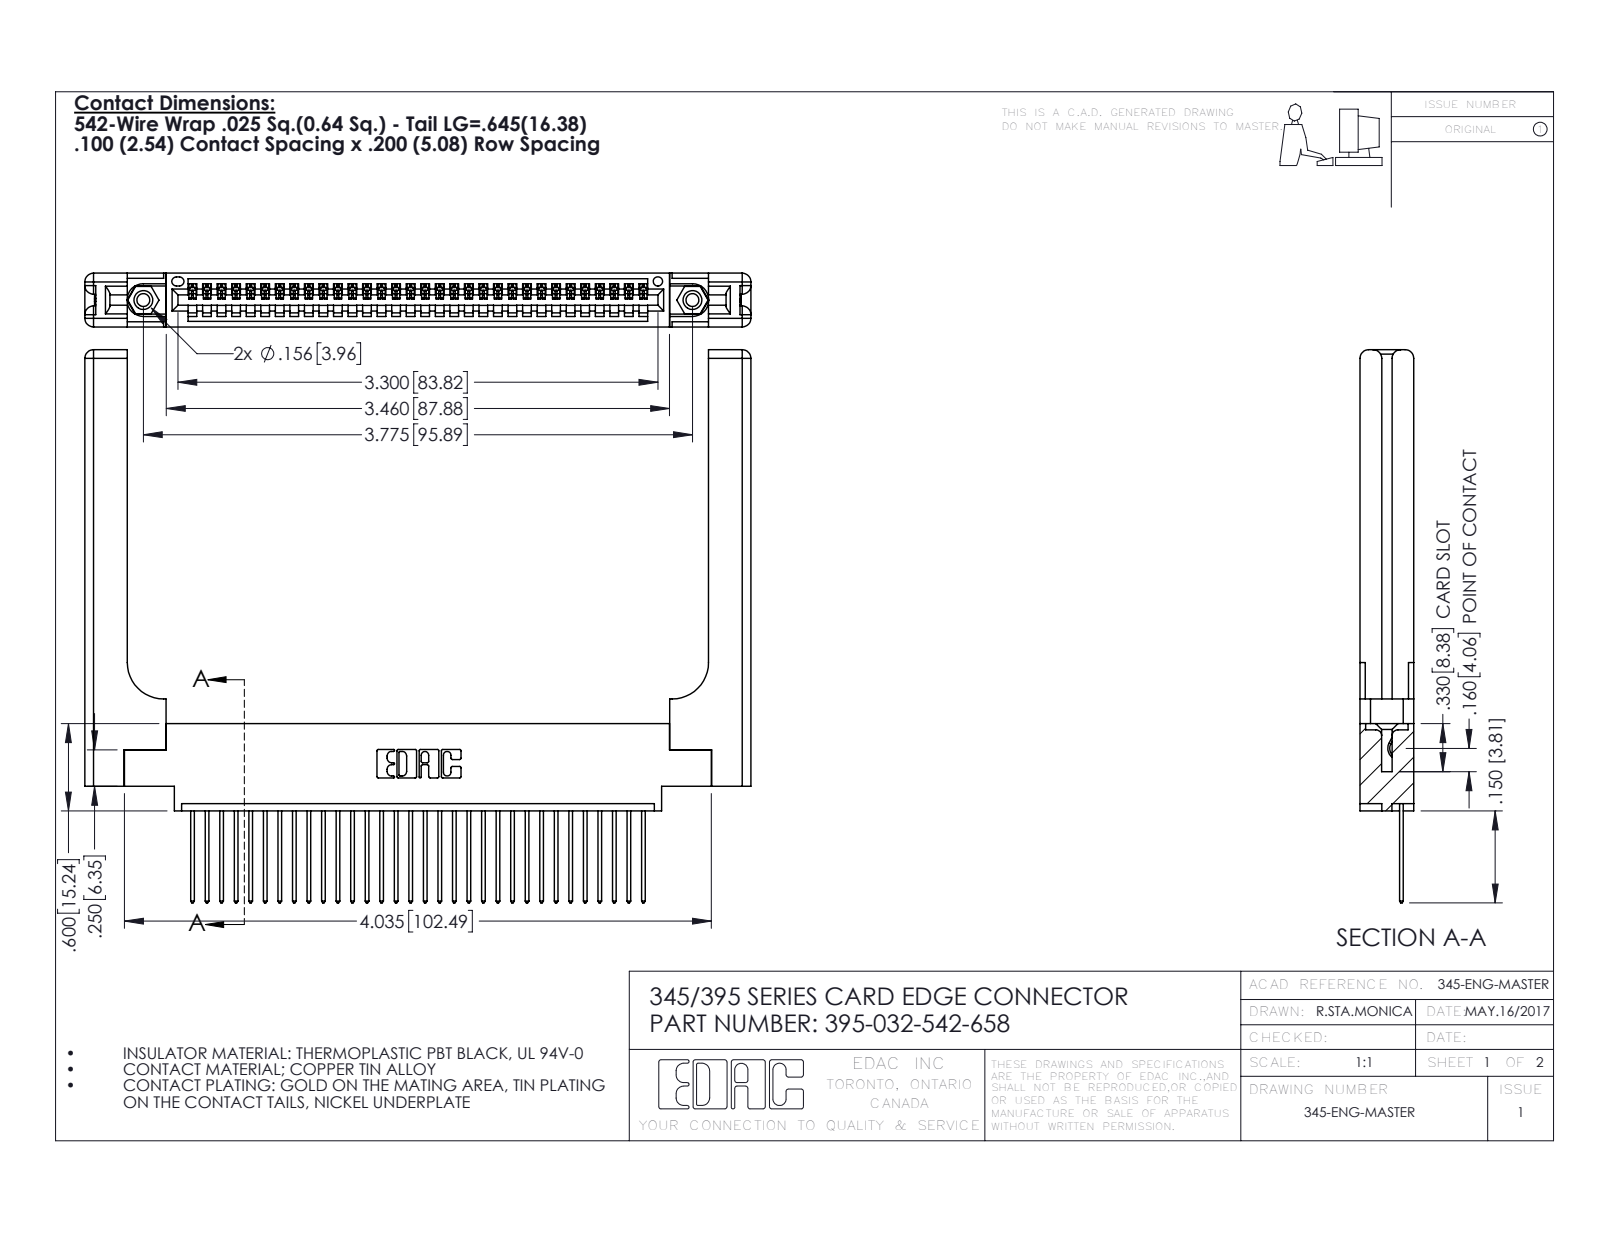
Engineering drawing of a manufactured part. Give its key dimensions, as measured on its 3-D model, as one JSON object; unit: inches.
{"part_name": "345-250-001_345-250-001-102; 345-292-001_345-293-142; 345-220-058_345-220-058; 345 Part_0.170 Offset - 0.156 Dia-TH (+1 more)", "step_written_by": "SolidWorks 2016 (CONFIG_CONTROL_DESIGN)", "units": "inches", "bodies": {"solids": 37, "faces": 2242, "planar": 1512, "cylindrical": 670, "other": 60}, "overall_size": [4.579, 3.802, 0.37], "volume_in3": 1.186, "surface_area_in2": 31.41, "round_holes": [[0.089, 2], [0.125, 2], [0.156, 2], [0.064, 1]], "round_bosses_or_shafts": [[0.155, 2]], "partial_cylinders_radius": [[0.006, 64], [0.01, 64], [0.01, 22], [0.06, 16], [0.007, 6], [0.031, 6], [0.026, 3], [0.03, 2]], "face_to_face_distances": [0.37, 0.072, 0.298, 0.098, 0.272, 0.025, 0.2, 0.148, 0.15, 0.077], "hole_center_spacings": [0.27, 3.54, 3.775]}
